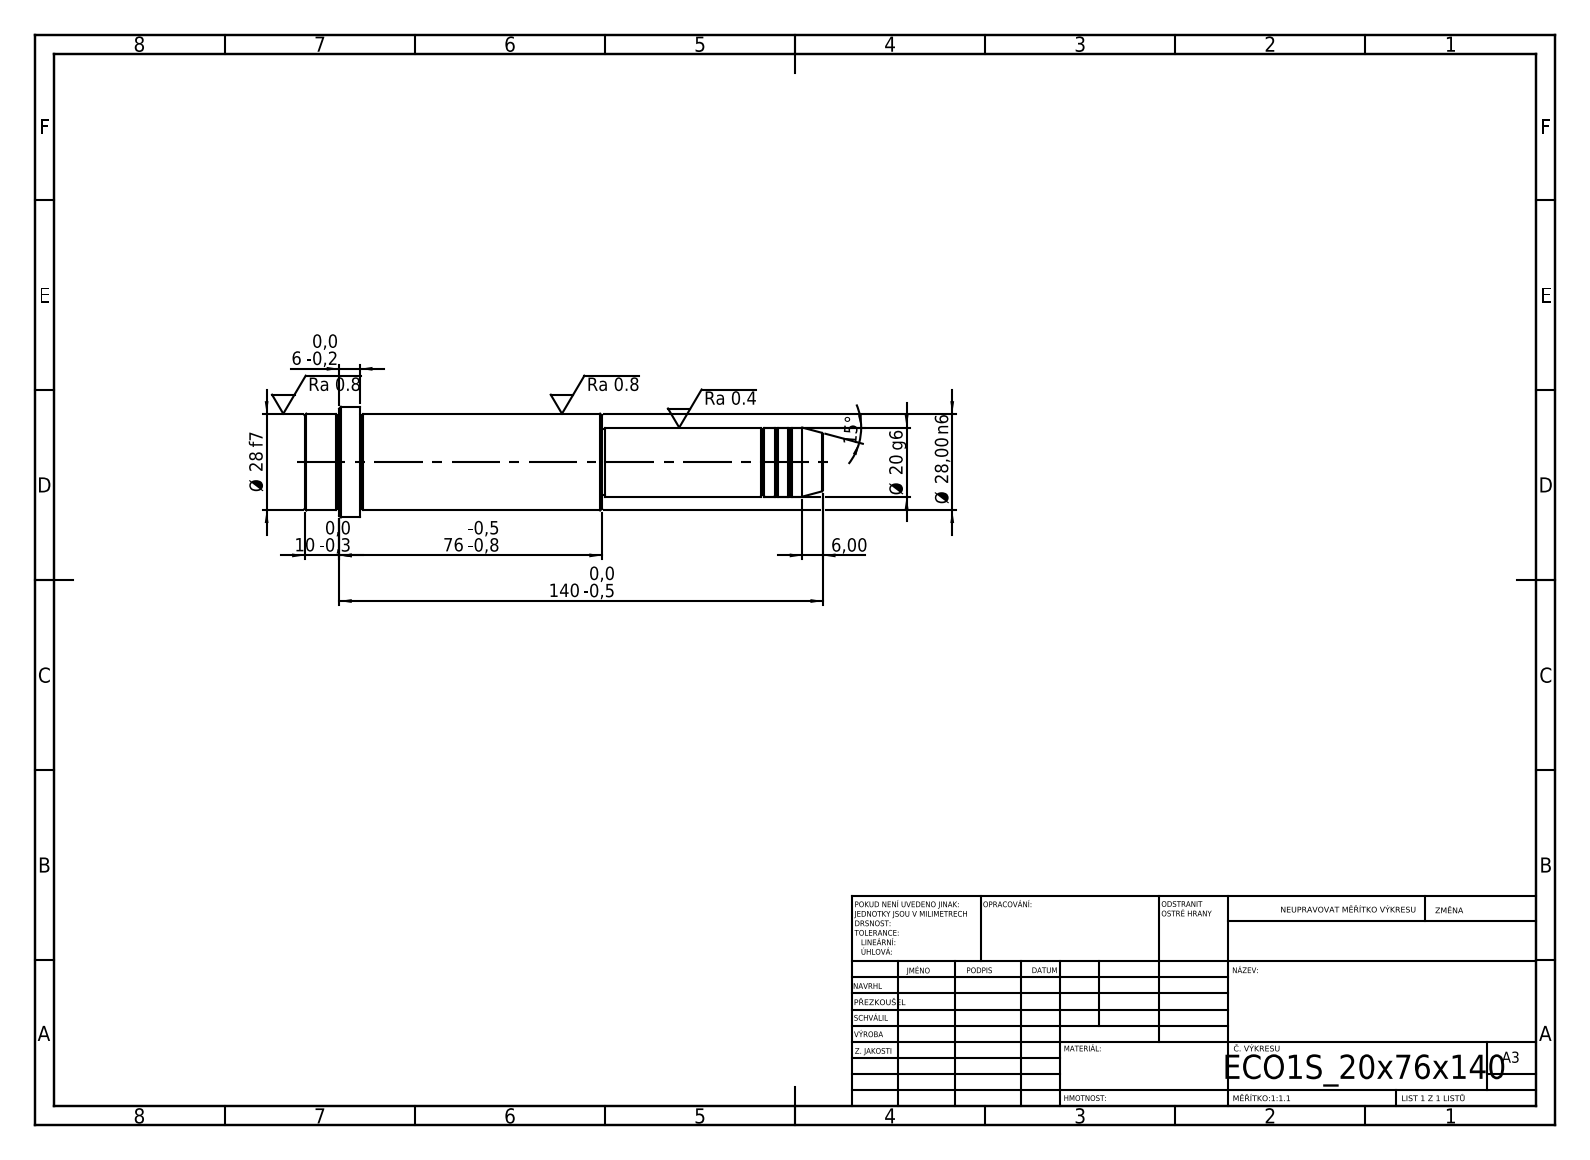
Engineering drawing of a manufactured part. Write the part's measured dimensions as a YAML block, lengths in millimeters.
step_written_by: "SolidWorks 2019 (CONFIG_CONTROL_DESIGN)"
units: millimeters
bodies: {solids: 1, faces: 52, planar: 6, cylindrical: 16, other: 30}
overall_size: [150, 32, 32]
volume: 73698
surface_area: 13322
round_bosses_or_shafts:
  - {diameter: 32, count: 1}
  - {diameter: 28, count: 1}
  - {diameter: 20, count: 1}
  - {diameter: 19, count: 1}
face_to_face_distances: [86, 64, 150, 134, 70, 16, 140, 76, 6, 10]
